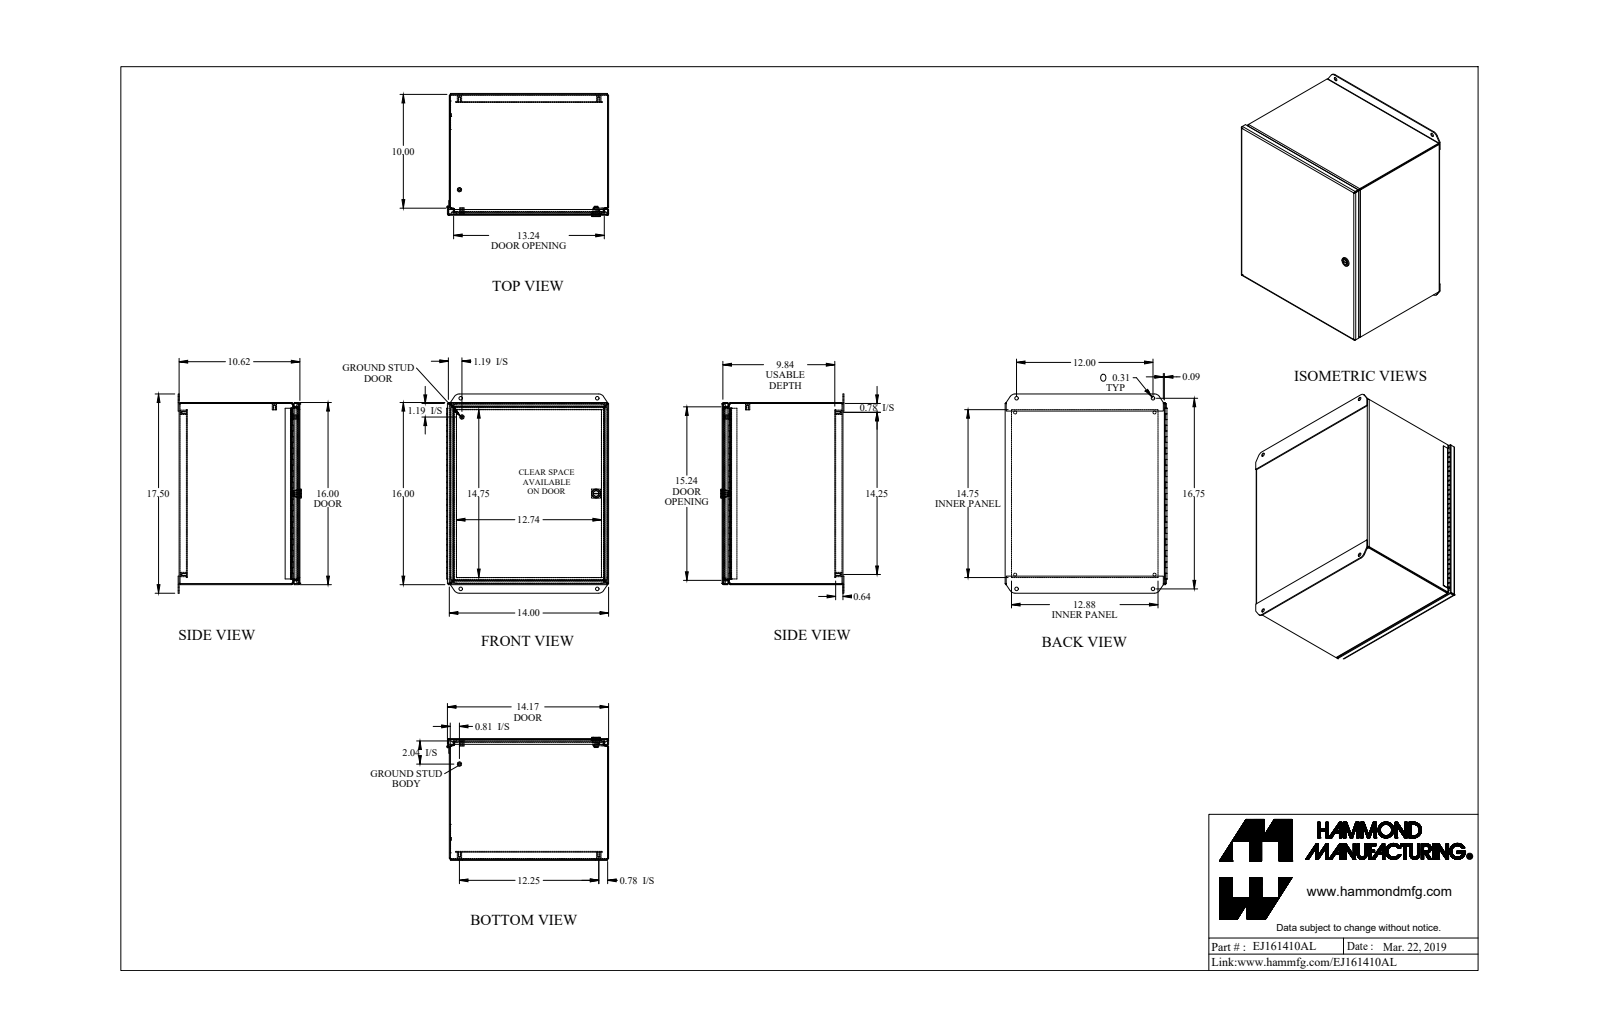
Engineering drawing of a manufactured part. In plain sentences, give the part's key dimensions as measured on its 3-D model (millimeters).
The part is named "EJ161410AL_Default". Its 3-D file was written by "SolidWorks 2019 (CONFIG_CONTROL_DESIGN)". It is 14 solids with 730 faces: 500 planar, 162 cylindrical and 68 other. Overall it measures 444.5 by 361.3 by 274.8 millimeters. Its volume is 1 850 000 cubic millimeters and its surface area 1 850 000 square millimeters. Round holes: 6 of diameter 4, 4 of diameter 6.7, 4 of diameter 8, 1 of diameter 13.1. Round bosses or shafts: 6 of diameter 9.5, 6 of diameter 8.4, 1 of diameter 20, 1 of diameter 13.6, 1 of diameter 12.6, 1 of diameter 11, 1 of diameter 4.6, 1 of diameter 2.5. Partial cylindrical surfaces (rounded edges, fillets, slot ends): 16 of radius 1, 16 of radius 3.1, 12 of radius 7.1, 4 of radius 6.4, 4 of radius 12.7, 4 of radius 12.7, 2 of radius 1.5, 1 of radius 0.8. The main face-to-face distances are 2.1, 267.6, 353.5, 404.3, 269.7, 265.6, 16.3, 14.3, 253.3, 251.3. The hole center spacings are 31.9, 309.6, 393.7, 499.8, 0.6, 181.1, 212.8, 304.8.
